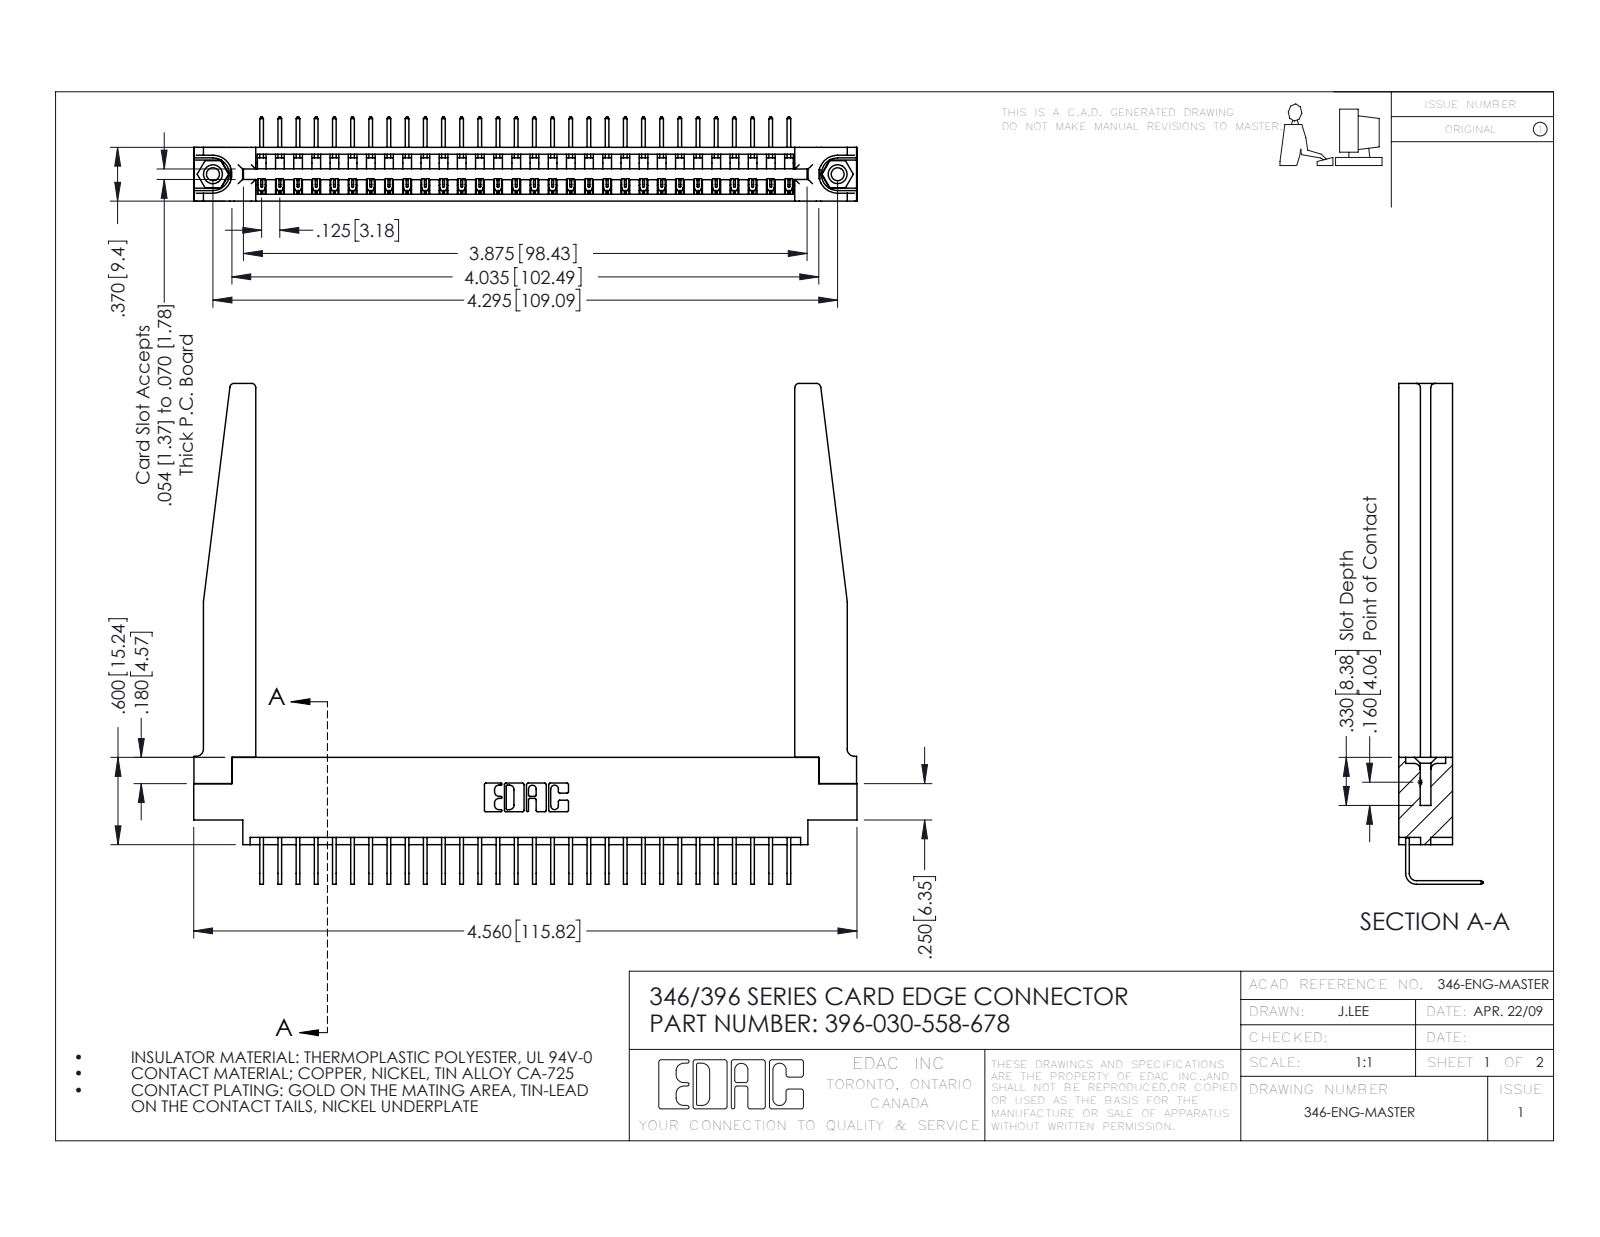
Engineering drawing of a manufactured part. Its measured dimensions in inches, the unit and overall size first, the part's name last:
Units: inches
Overall size (bounding box): 4.56 × 3.443 × 0.58
Round holes (diameter × count): ⌀0.089 ×2, ⌀0.125 ×2, ⌀0.156 ×2, ⌀0.064 ×1
Round bosses / shafts (diameter × count): ⌀0.155 ×2
Partial cylindrical surfaces — rounded edges, fillets, slot ends (radius × count): R0.006 ×60, R0.01 ×22, R0.03 ×8, R0.007 ×6, R0.031 ×6, R0.026 ×3, R0.05 ×3, R0.031 ×2
Main face-to-face distances: 0.37, 0.322, 0.048, 0.072, 0.148, 0.15, 0.25, 0.298, 0.025, 0.222
Hole centre spacings: 0.246, 4.087, 4.295
Volume: 1.09 in³ · Surface area: 32.32 in²
Bodies: 35 solids, 2160 faces (1482 planar, 626 cylindrical, 52 other)
Part name (STEP PRODUCT): 346-220-078_345-220-078; 346 Part_0.170 Offset - 0.156 Dia-TH; 345-292-001_558 Tail - 2; 396-030-558-678 (+1 more)
STEP written by: SolidWorks 2016 (CONFIG_CONTROL_DESIGN)
